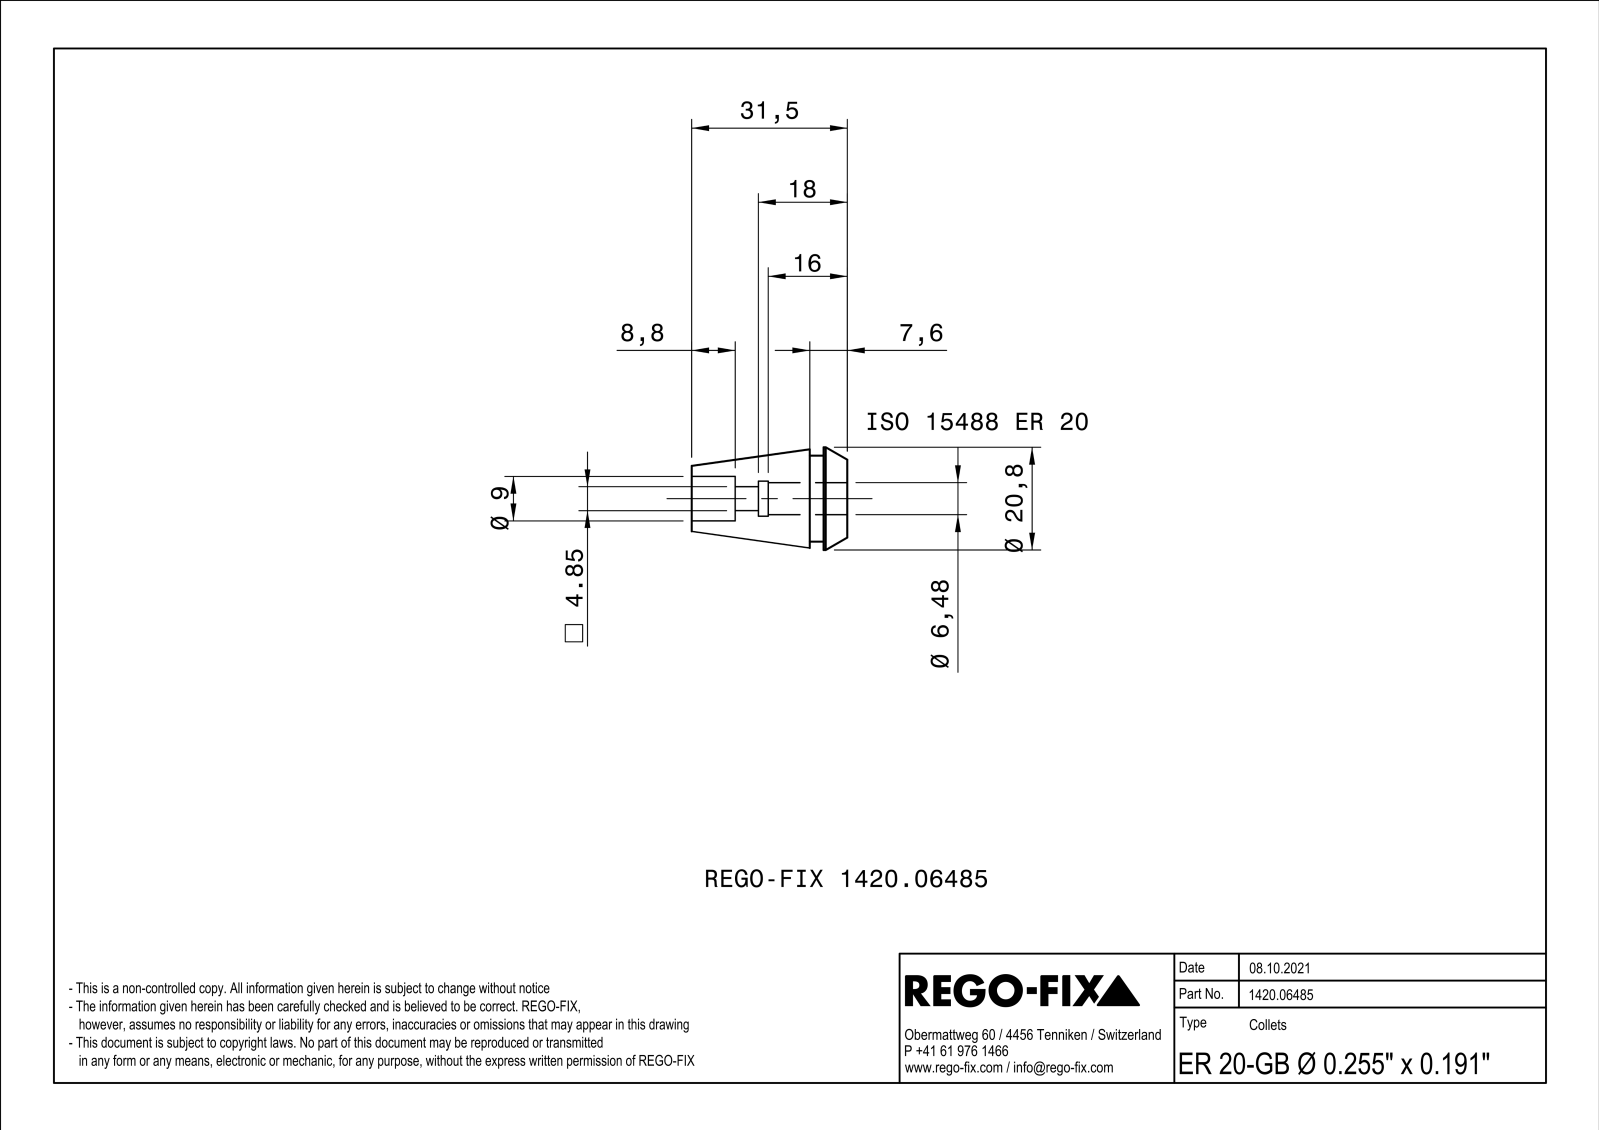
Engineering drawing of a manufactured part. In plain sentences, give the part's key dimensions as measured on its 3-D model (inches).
The part is named "NOCUT". Its 3-D file was written by "SIEMENS PLM Software Solid Edge ST10 (AUTOMOTIVE_DESIGN)". It is 1 solid with 160 faces: 60 planar, 36 cylindrical and 64 other. Overall it measures 1.24 by 0.819 by 0.819 inches. Its volume is 0.308 cubic inches and its surface area 7.218 square inches. Round holes: 1 of diameter 0.255, 1 of diameter 0.354. Round bosses or shafts: 1 of diameter 0.685. Partial cylindrical surfaces (rounded edges, fillets, slot ends): 1 of radius 0.112, 1 of radius 0.134, 1 of radius 0.14. The main face-to-face distances are 0.031, 0.189, 1.24, 1.051, 0.091, 0.122, 0.299, 0.11, 0.941, 0.894.
